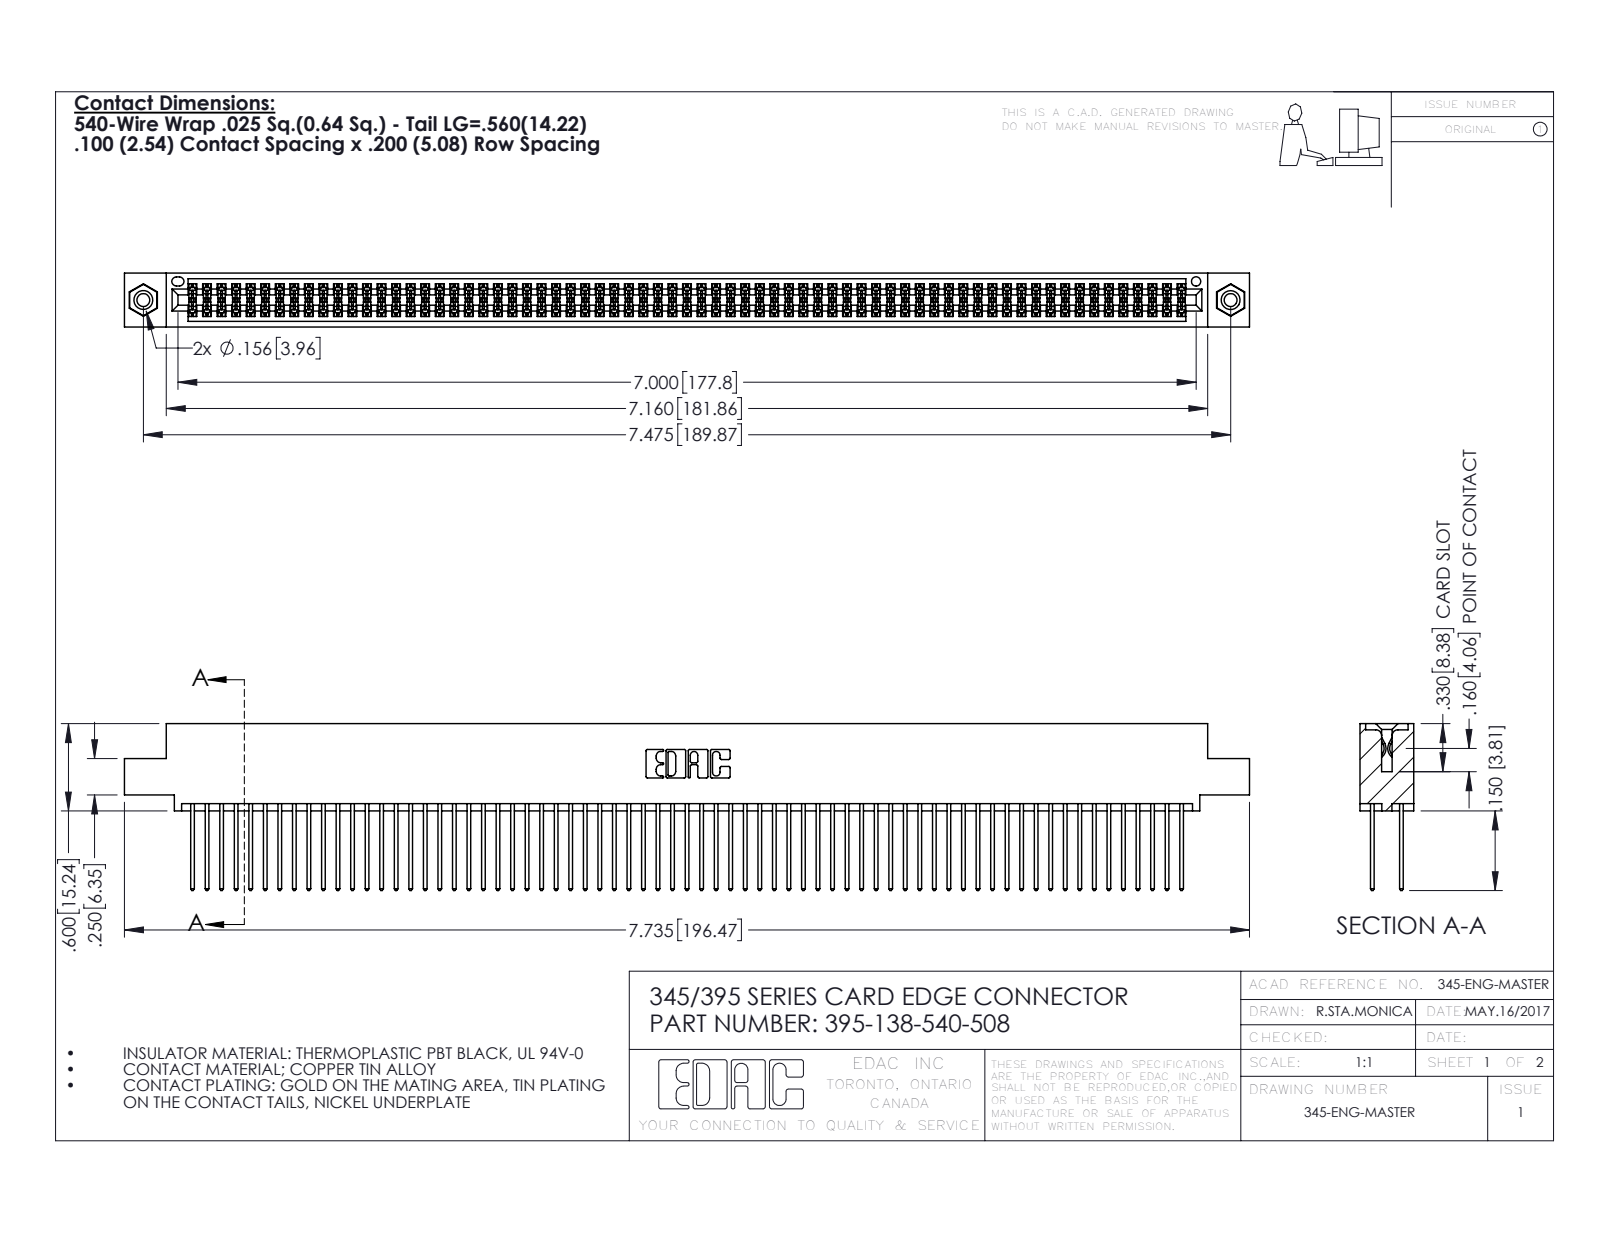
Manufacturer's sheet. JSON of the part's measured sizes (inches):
{"part_name": "345-292-001_345-293-140; 345 Part_0.110 Offset - 0.156 Dia-TI; 395-138-540-508; 345-250-001_345-250-003-102", "step_written_by": "SolidWorks 2016 (CONFIG_CONTROL_DESIGN)", "units": "inches", "bodies": {"solids": 141, "faces": 7090, "planar": 4670, "cylindrical": 2404, "other": 16}, "overall_size": [7.735, 1.147, 0.37], "volume_in3": 1.207, "surface_area_in2": 50.05, "round_holes": [[0.089, 2], [0.125, 2], [0.156, 2], [0.064, 1]], "round_bosses_or_shafts": [[0.155, 2]], "partial_cylinders_radius": [[0.006, 207], [0.01, 138], [0.01, 22], [0.007, 6], [0.031, 6], [0.026, 3], [0.014, 2], [0.019, 2]], "face_to_face_distances": [0.072, 0.298, 0.2, 0.098, 0.272, 0.025, 0.225, 0.37, 0.175, 0.149], "hole_center_spacings": [0.27, 7.239, 7.475]}
